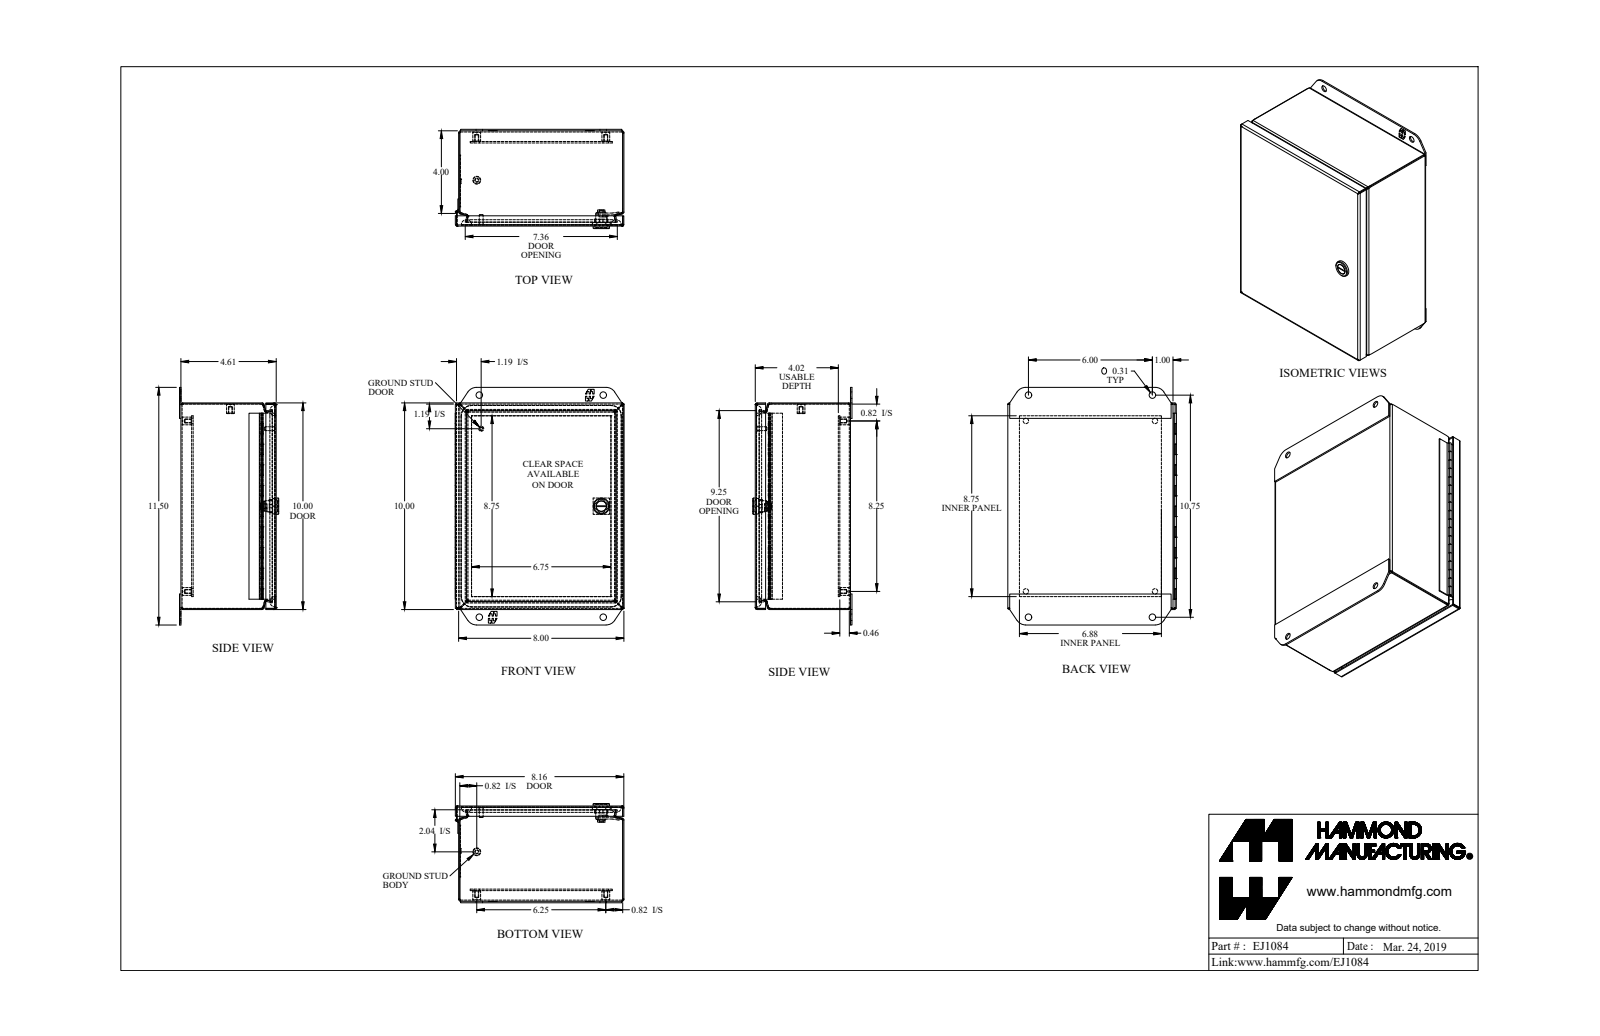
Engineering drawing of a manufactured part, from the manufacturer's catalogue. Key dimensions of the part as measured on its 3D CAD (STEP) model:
Part name (STEP PRODUCT): EJ1084_Default
STEP written by: SolidWorks 2019 (CONFIG_CONTROL_DESIGN)
Units: inches
Bodies: 16 solids, 675 faces (377 planar, 206 cylindrical, 92 other)
Overall size (bounding box): 11.5 × 8.165 × 4.805
Volume: 29.4 in³ · Surface area: 966.9 in²
Round holes (diameter × count): ⌀0.156 ×5, ⌀0.265 ×4, ⌀0.313 ×4, ⌀0.05 ×1, ⌀0.516 ×1
Round bosses / shafts (diameter × count): ⌀0.375 ×5, ⌀0.788 ×1, ⌀0.535 ×1, ⌀0.496 ×1, ⌀0.435 ×1, ⌀0.25 ×1, ⌀0.188 ×1, ⌀0.1 ×1
Partial cylindrical surfaces — rounded edges, fillets, slot ends (radius × count): R0.029 ×16, R0.086 ×16, R0.281 ×10, R0.25 ×4, R0.499 ×4, R0.5 ×4, R0.06 ×2, R0.539 ×2
Main face-to-face distances: 0.057, 4.554, 0.072, 0.589, 4.611, 4.497, 7.943, 9.943, 0.46, 0.517
Hole centre spacings: 1.256, 1.257, 4.131, 6, 6.25, 6.251, 6.252, 7.307
